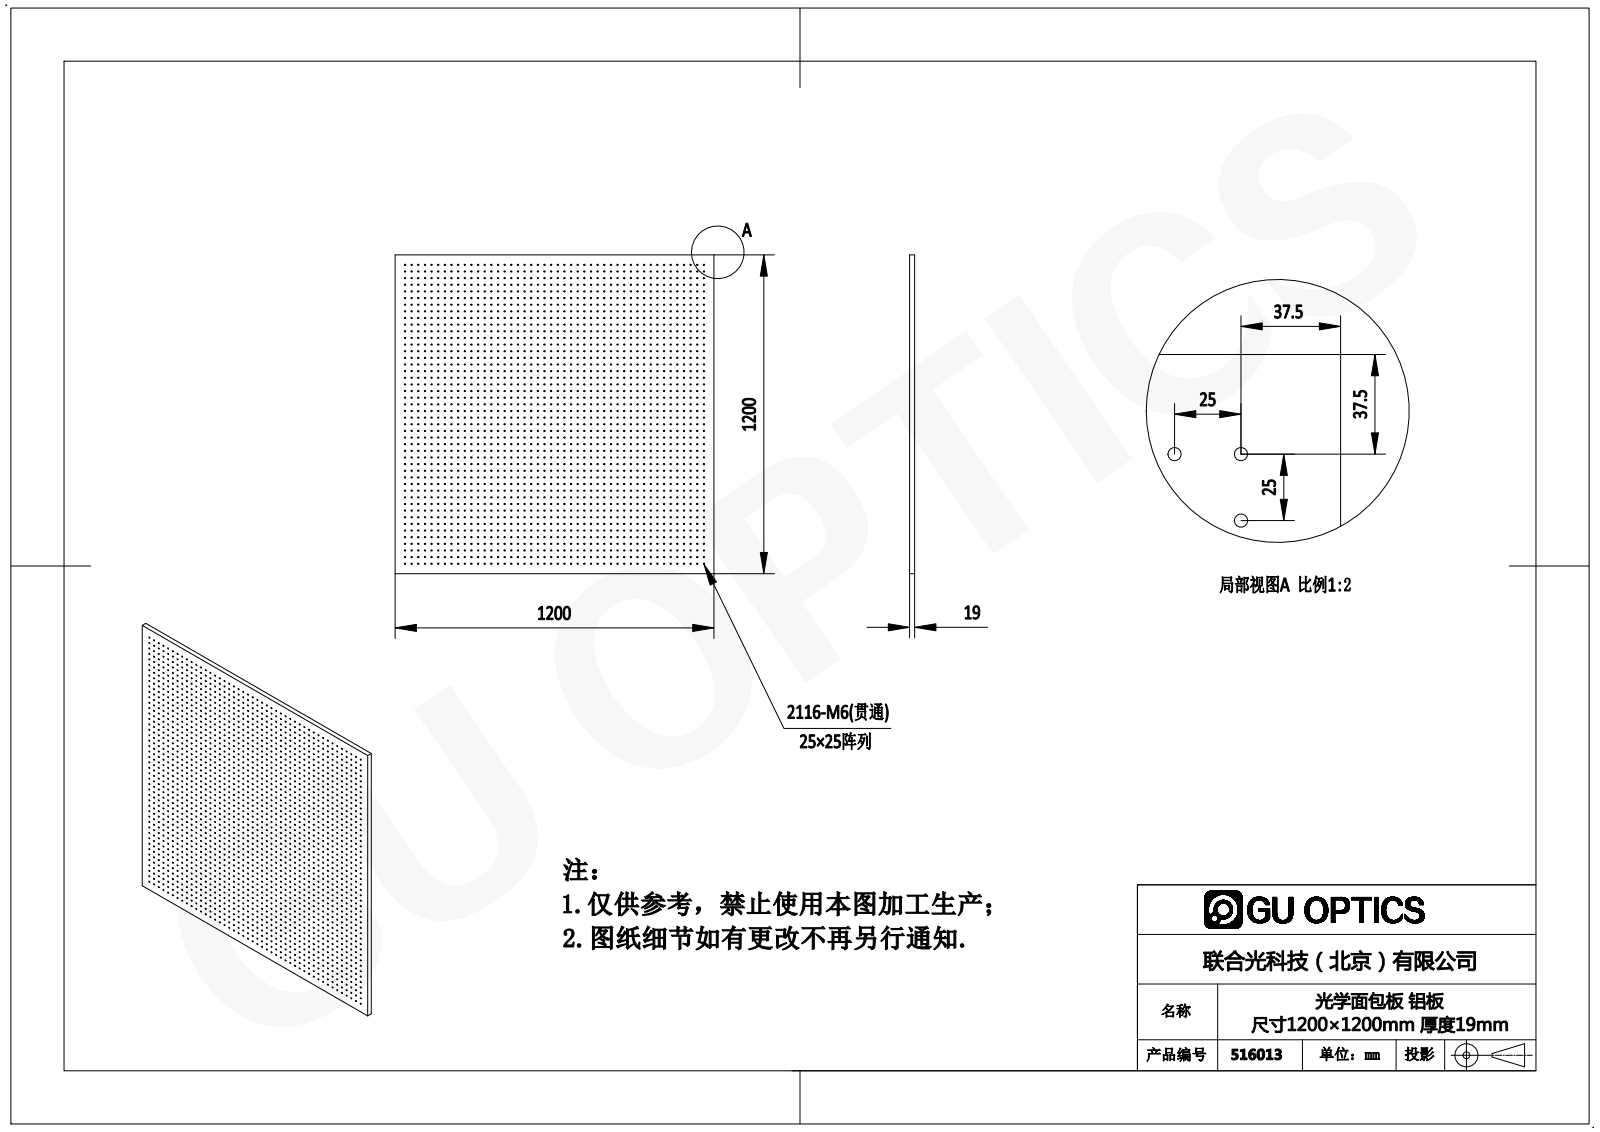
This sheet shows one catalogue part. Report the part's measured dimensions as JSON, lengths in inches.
{"part_name": "516013", "step_written_by": "SolidWorks 2016 (AUTOMOTIVE_DESIGN)", "units": "inches", "bodies": {"solids": 1, "faces": 4238, "planar": 6, "cylindrical": 4232, "other": 0}, "overall_size": [47.244, 47.244, 0.748], "volume_in3": 1621, "surface_area_in2": 5456, "round_holes": [[0.197, 2116]], "face_to_face_distances": [0.748, 47.244], "hole_center_spacings": [0.984, 1.969, 2.953, 3.937, 4.921, 5.906, 6.89, 7.874]}
